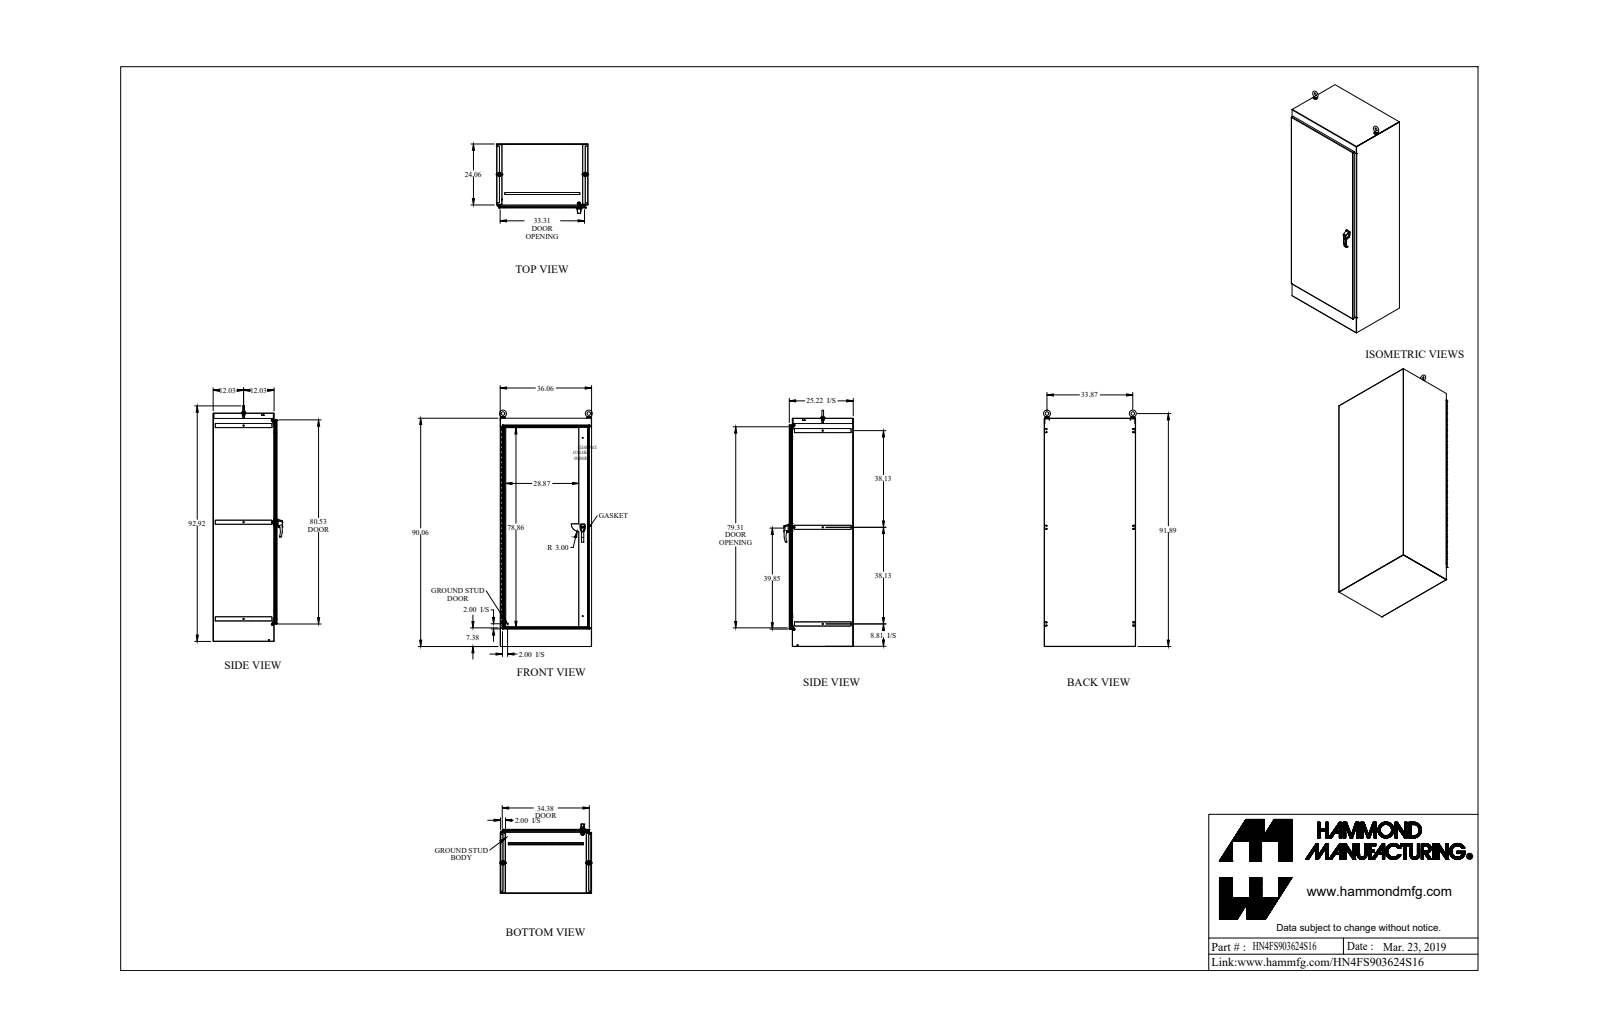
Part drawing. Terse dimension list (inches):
name: HN4FS903624S16
written by: SolidWorks 2018 (AUTOMOTIVE_DESIGN)
unit: in
bodies: 57 solids, 2060 faces (940 planar, 955 cylindrical, 165 other)
size: 93.489 × 36.604 × 27.362
volume: 1 401 in³; area: 29 557 in²
holes: 13× ⌀0.304, 7× ⌀0.35, 3× ⌀0.5, 2× ⌀0.25, 2× ⌀0.257, 2× ⌀0.28, 2× ⌀0.281, 2× ⌀0.313, 2× ⌀0.39, 2× ⌀0.413, 2× ⌀0.527, 2× ⌀0.68
bosses: 2× ⌀1.75, 2× ⌀1.5, 2× ⌀1.25, 2× ⌀1, 2× ⌀0.75, 2× ⌀0.738, 2× ⌀0.63, 2× ⌀0.625
rounds: 42× R0.043, 36× R0.138, 23× R0.5, 22× R0.125, 16× R0.018, 15× R0.06, 13× R0.048, 13× R0.143
face distances: 0.095, 25.152, 35.965, 25.057, 25.247, 35.87, 36.06, 89.965, 23.965, 1.187
hole spacings: 6, 12, 18, 24, 30, 36, 42, 48
